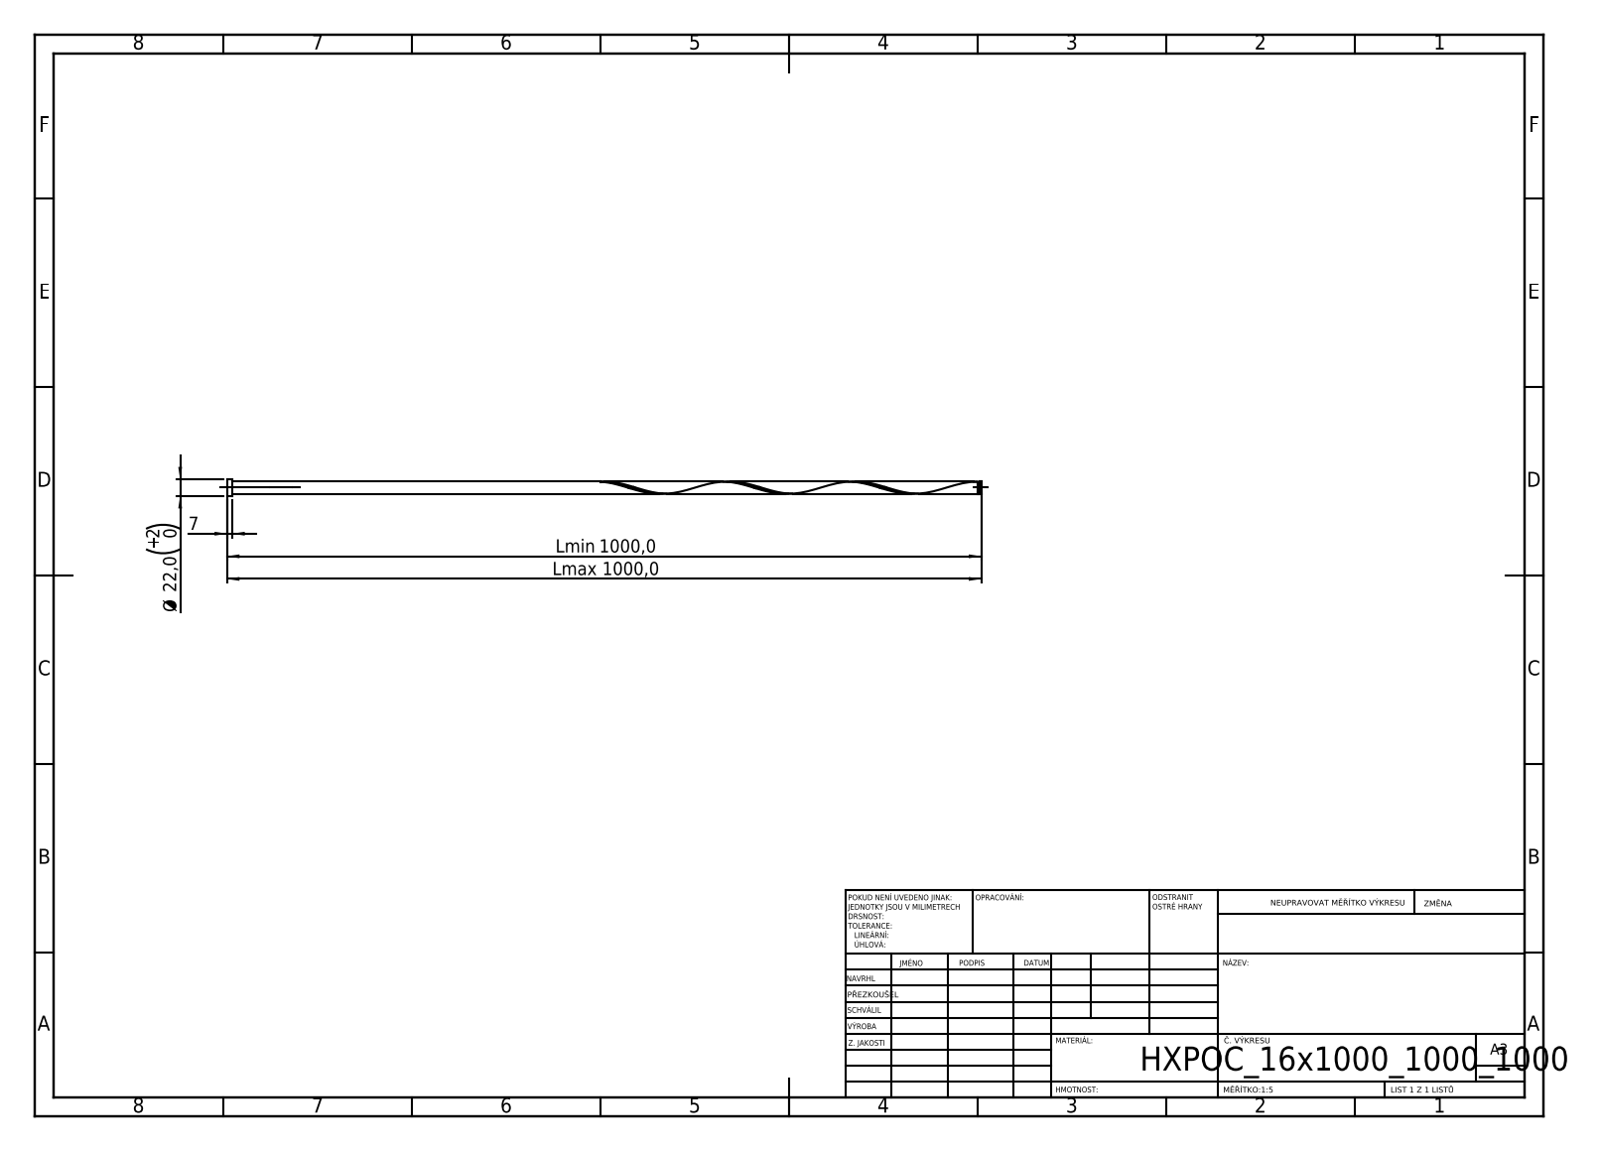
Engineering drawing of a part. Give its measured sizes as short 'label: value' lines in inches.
written by: SolidWorks 2019 (CONFIG_CONTROL_DESIGN)
unit: in
bodies: 1 solid, 16 faces (6 planar, 9 cylindrical, 1 other)
size: 39.37 × 0.866 × 0.866
volume: 14.94 in³; area: 106.7 in²
bosses: 1× ⌀0.866, 1× ⌀0.63, 1× ⌀0.504
face distances: 39.37, 0.276, 39.094, 39.31, 39.034, 0.06, 39.184, 38.908, 0.126, 0.186
